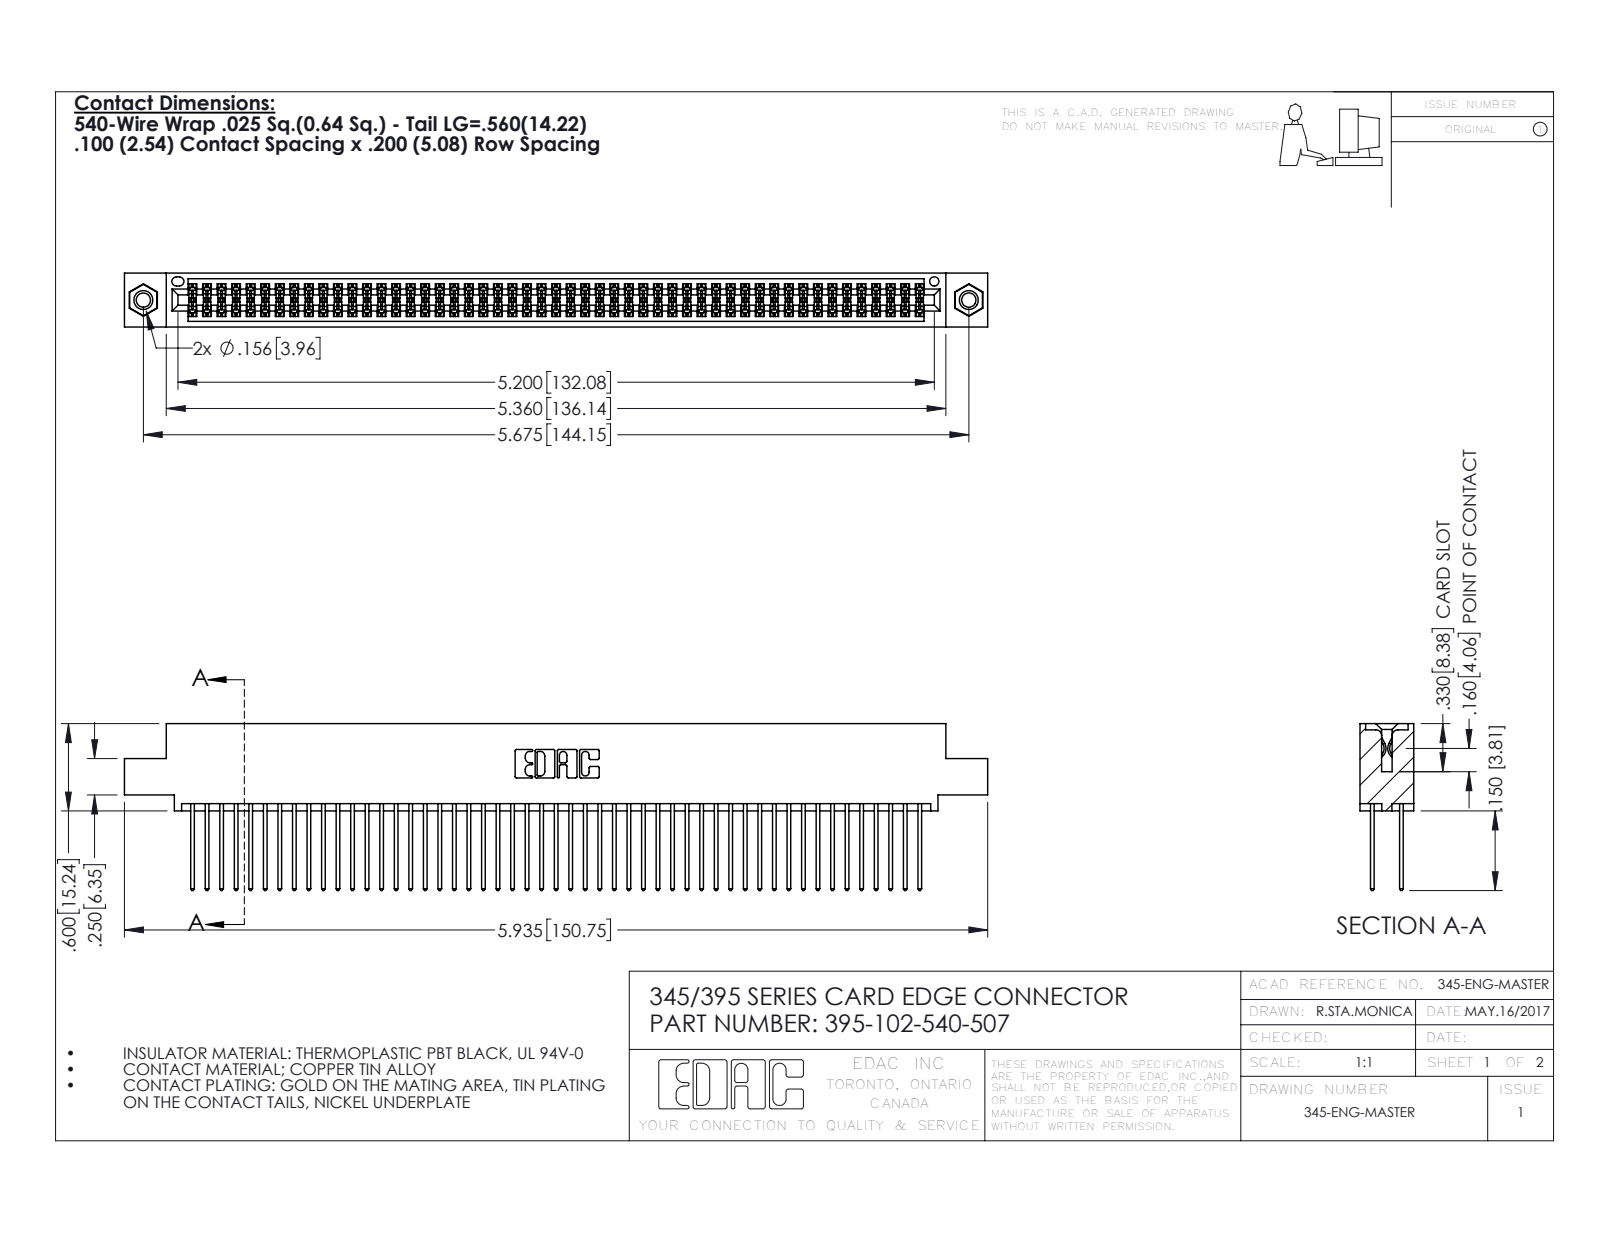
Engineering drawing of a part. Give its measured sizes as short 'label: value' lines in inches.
name: 345 Part_0.110 Offset - 0.156 Dia-TI; 345-250-001_345-250-005-103; 345-292-001_345-293-140; 395-102-540-507
written by: SolidWorks 2016 (CONFIG_CONTROL_DESIGN)
unit: in
bodies: 105 solids, 5290 faces (3482 planar, 1792 cylindrical, 16 other)
size: 5.935 × 1.147 × 0.37
volume: 0.917 in³; area: 37.67 in²
holes: 2× ⌀0.098, 2× ⌀0.125, 2× ⌀0.156, 1× ⌀0.064
bosses: 2× ⌀0.155
rounds: 153× R0.006, 102× R0.01, 22× R0.01, 6× R0.007, 6× R0.031, 3× R0.026, 2× R0.014, 2× R0.019
face distances: 0.072, 0.298, 0.2, 0.098, 0.272, 0.025, 0.37, 0.225, 0.175, 0.149
hole spacings: 0.27, 5.439, 5.675
